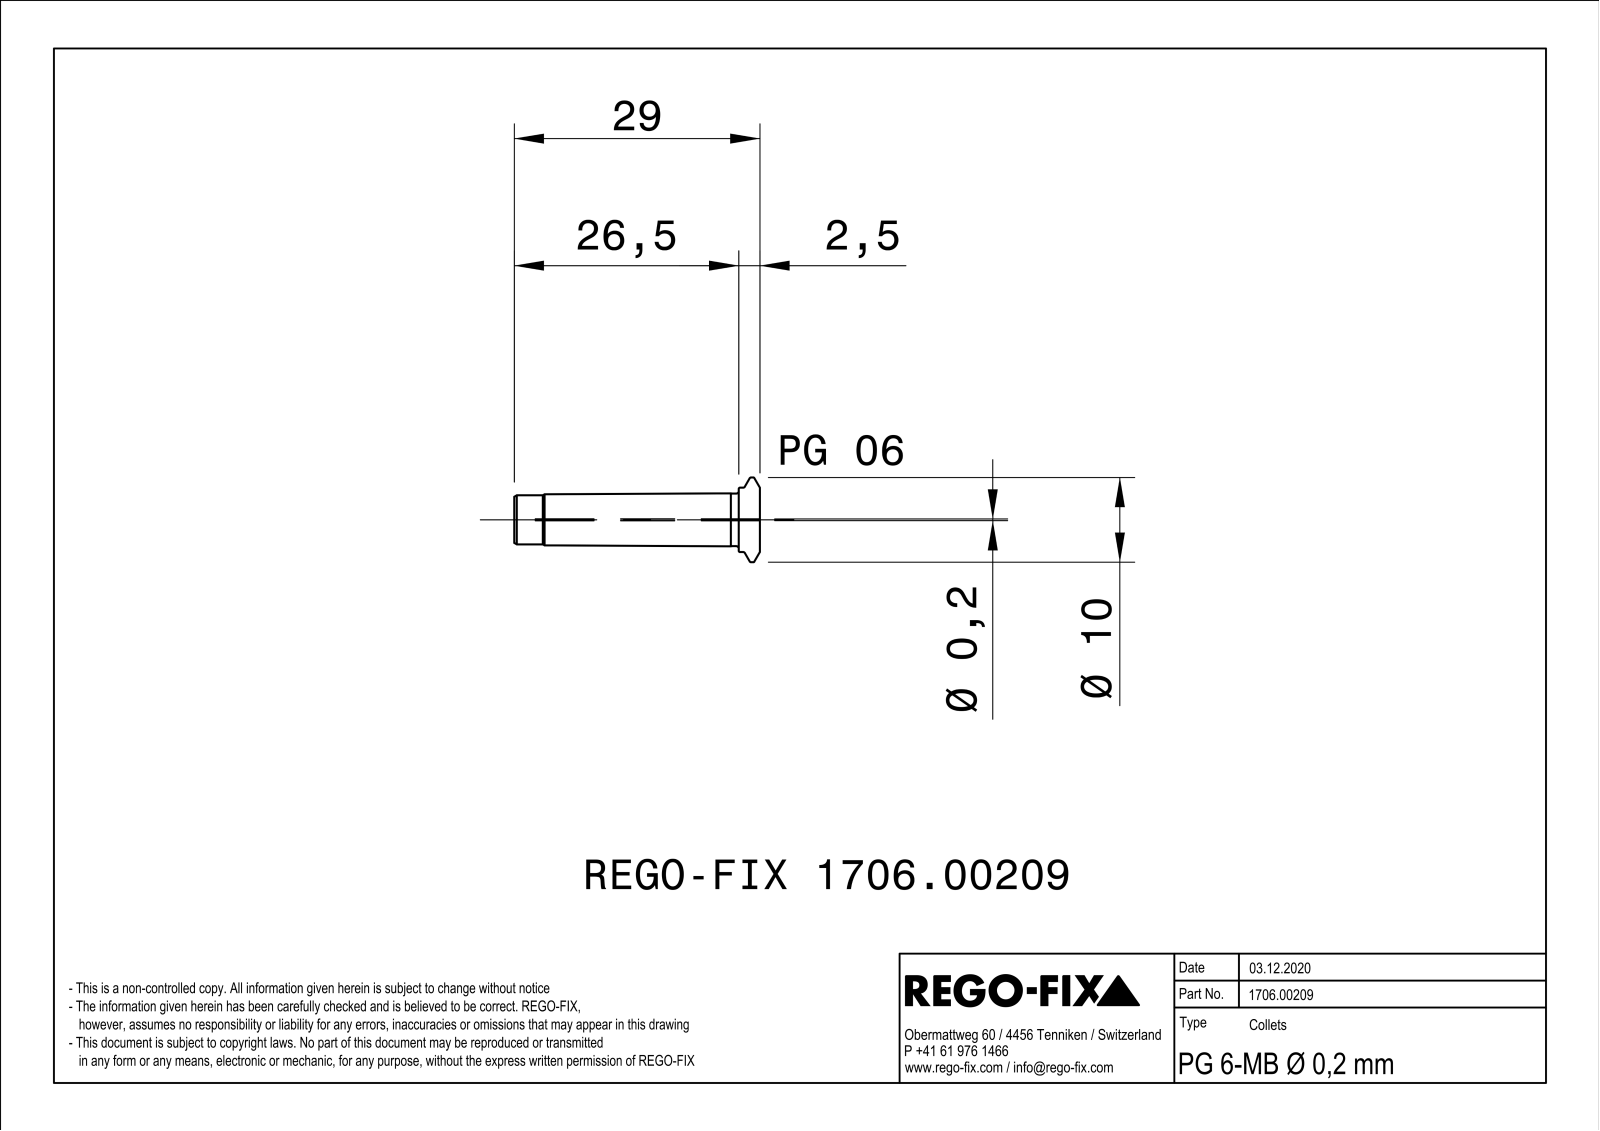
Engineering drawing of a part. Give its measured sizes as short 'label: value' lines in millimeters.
name: NOCUT
written by: SIEMENS PLM Software Solid Edge ST10 (AUTOMOTIVE_DESIGN)
unit: mm
bodies: 1 solid, 76 faces (18 planar, 18 cylindrical, 40 other)
size: 29 × 10 × 9.99
volume: 633 mm³; area: 1 391 mm²
holes: 3× ⌀1.5, 1× ⌀0.2
bosses: 1× ⌀10, 1× ⌀7.6, 1× ⌀6.2, 1× ⌀5.8
rounds: 1× R1.73
face distances: 0.45, 0.46, 20, 29, 9, 2.5, 17.5, 26.5
hole spacings: 3.22, 1.92, 1.75
